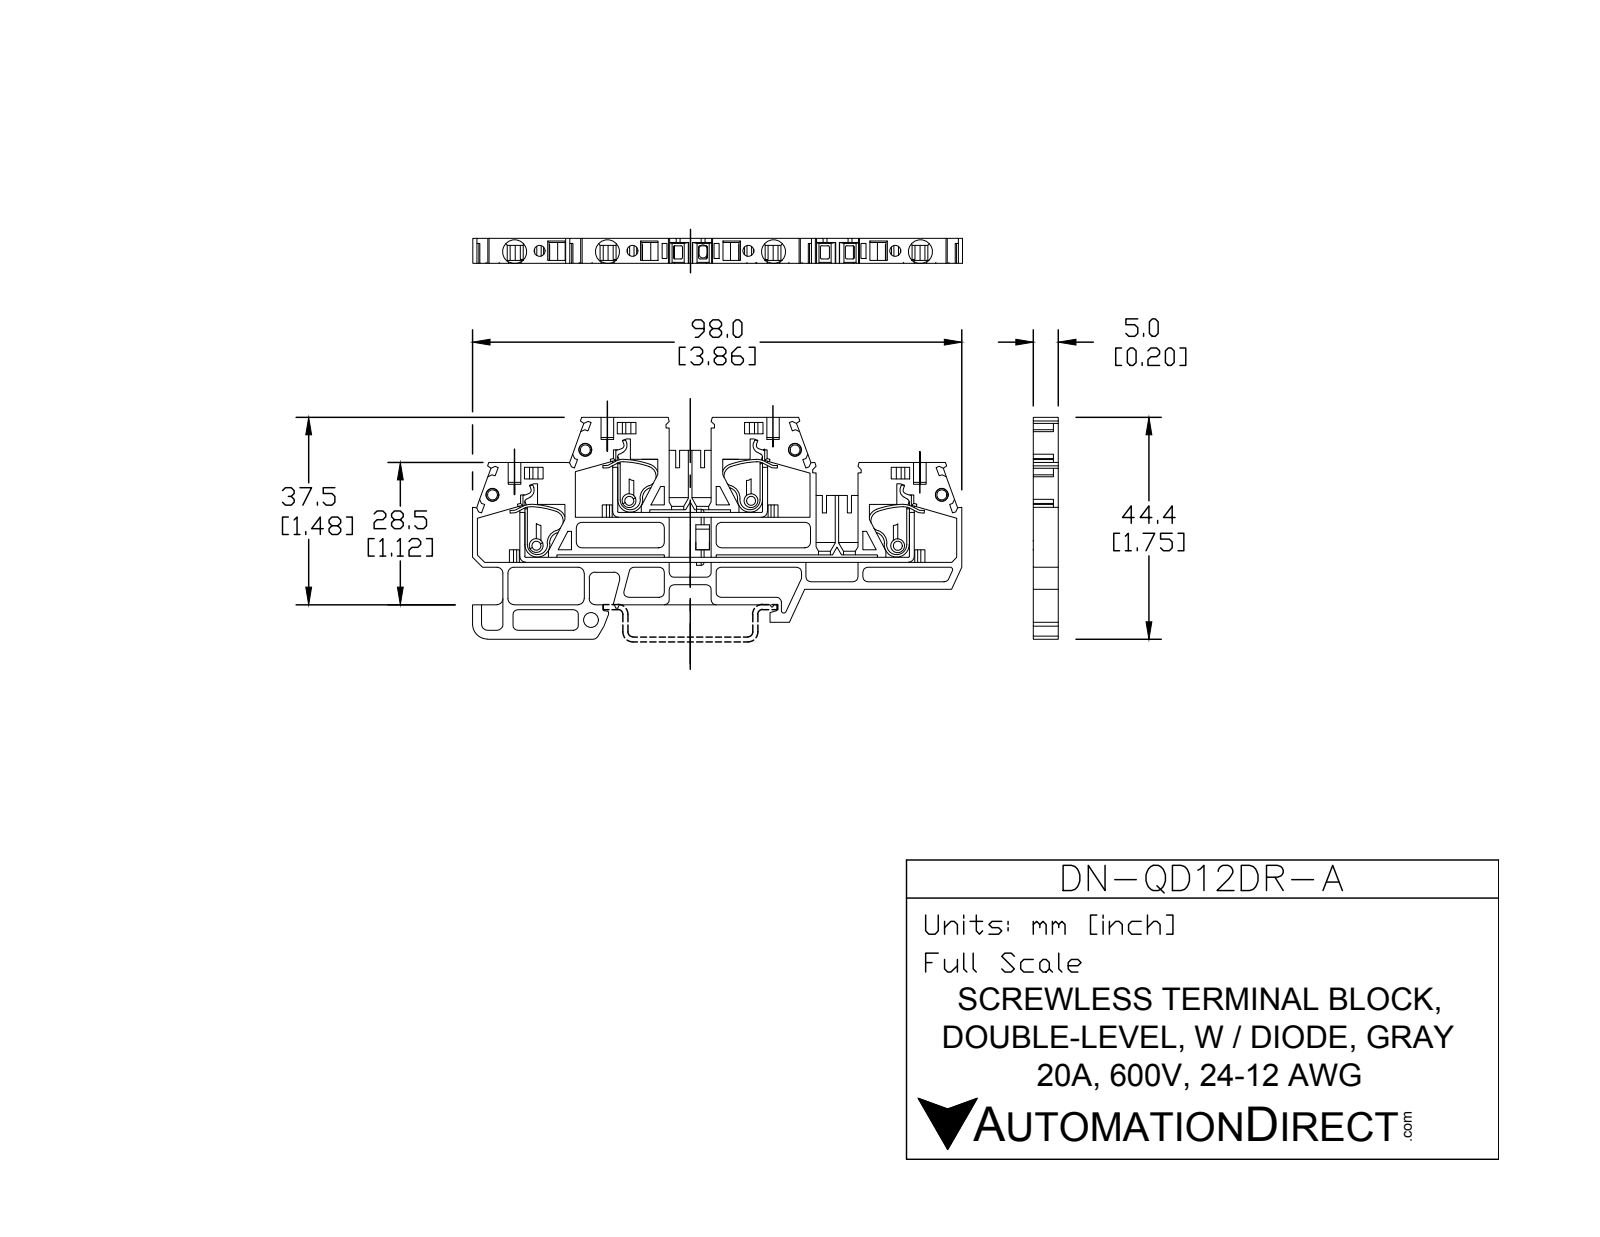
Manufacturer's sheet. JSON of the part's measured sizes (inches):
{"part_name": "DN-QD12DR-A", "step_written_by": "SolidWorks 2017 (AUTOMOTIVE_DESIGN)", "units": "inches", "bodies": {"solids": 1, "faces": 713, "planar": 536, "cylindrical": 129, "other": 48}, "overall_size": [3.858, 1.748, 0.197], "volume_in3": 0.399, "surface_area_in2": 19.43, "round_holes": [[0.087, 4], [0.102, 4], [0.189, 4], [0.118, 1]], "round_bosses_or_shafts": [[0.11, 4]], "partial_cylinders_radius": [[0.039, 23], [0.047, 12], [0.043, 8], [0.02, 4], [0.028, 4], [0.055, 4], [0.012, 1], [0.118, 1]], "face_to_face_distances": [0.197, 0.039, 0.031, 0.165, 0.079, 0.118, 0.114, 0.028, 0.394, 0.059], "hole_center_spacings": [0.197, 0.732, 1.11, 1.157, 1.843, 2.268, 3, 0.535]}
